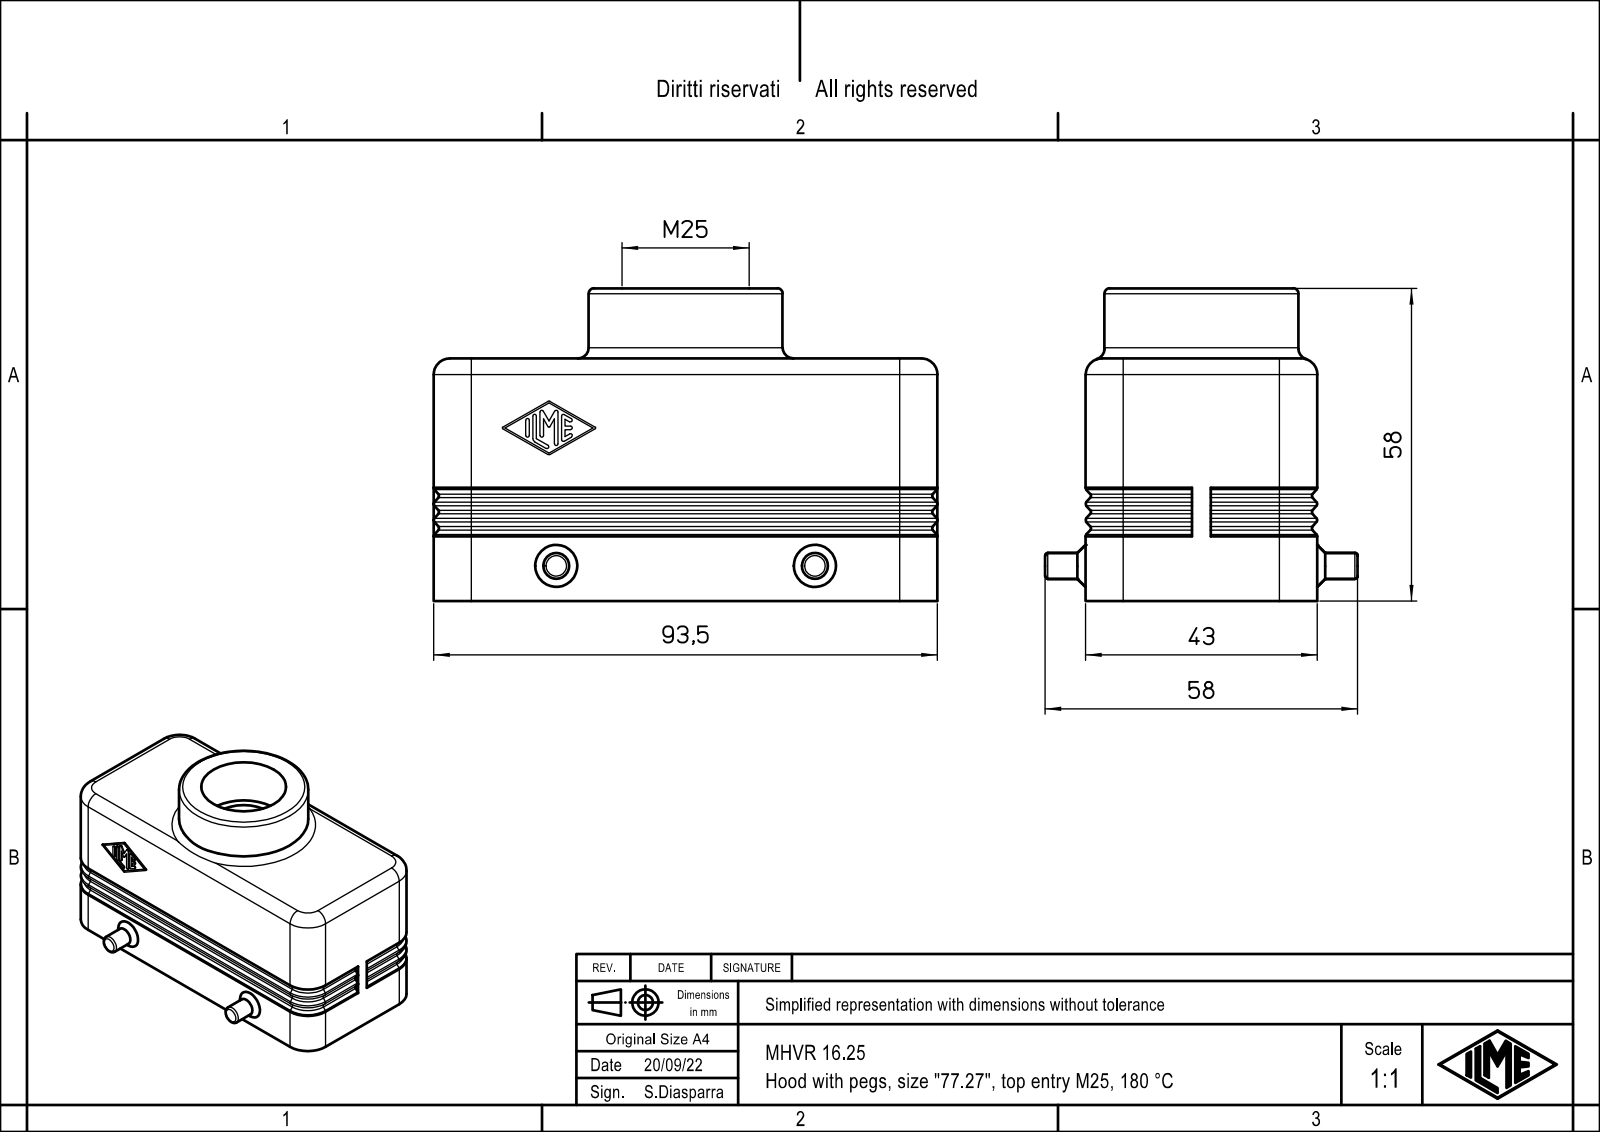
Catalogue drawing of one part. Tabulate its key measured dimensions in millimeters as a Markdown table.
| quantity | value |
| --- | --- |
| part name | MHVR_16.25 |
| STEP written by | PTC Creo Elements/Direct Modeling 19.0B 21-Mar-2015 (C) Parametric Technology GmbH (AUTOMOTIVE_DESIGN) |
| units | millimeters |
| bodies | 1 solid, 280 faces (148 planar, 86 cylindrical, 46 other) |
| overall size | 93.5 × 58 × 55 |
| volume | 58 440 mm³ |
| surface area | 32 963 mm² |
| round holes (diameter × count) | 2.46 × 4, 4 × 4, 24.5 × 1, 25 × 1 |
| round bosses / shafts (diameter × count) | 5 × 2, 36 × 1 |
| partial cylindrical surfaces (radius × count) | 0.25 × 14, 3 × 8, 2 × 4, 5.3 × 4, 6 × 4, 1.5 × 1 |
| main face-to-face distances | 3, 40, 37, 43, 11.5, 8.5, 90.5, 20, 93.5, 87.5 |
| hole center spacings | 41.03, 27, 77.5, 82.07 |
